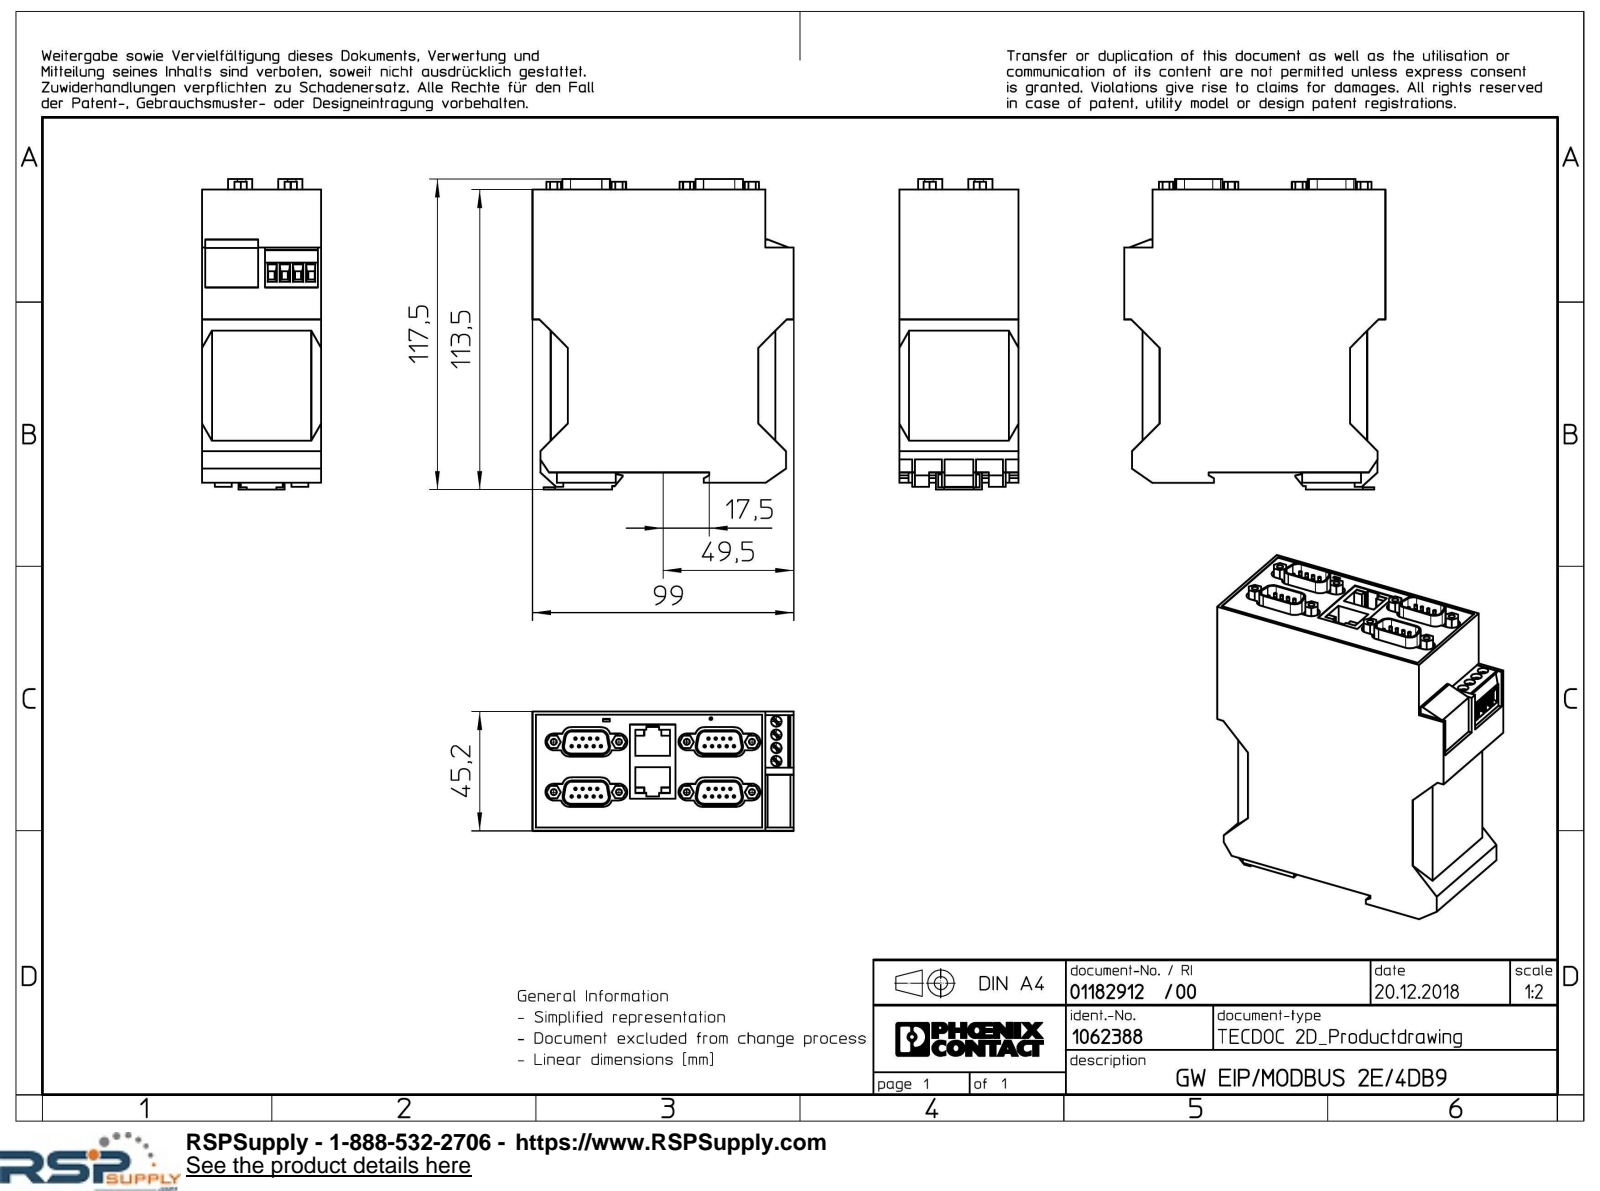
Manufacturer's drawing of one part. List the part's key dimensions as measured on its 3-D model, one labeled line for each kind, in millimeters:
Part name (STEP PRODUCT): GW_EIP_MODBUS_2E_4DB9-select
STEP written by: Creo Elements/Direct Modeling 18.1I 14-Aug-2016 (C) Parametric Technology GmbH (AUTOMOTIVE_DESIGN)
Units: millimetres
Bodies: 1 solid, 568 faces (414 planar, 154 cylindrical, 0 other)
Overall size (bounding box): 117.5 × 99 × 45.2
Volume: 437 141 mm³ · Surface area: 45 719 mm²
Round holes (diameter × count): ⌀2.29 ×8, ⌀4 ×4, ⌀1.08 ×1
Round bosses / shafts (diameter × count): ⌀1 ×36
Partial cylindrical surfaces — rounded edges, fillets, slot ends (radius × count): R3.17 ×24, R2.54 ×16, R3.04 ×16
Main face-to-face distances: 45.2, 4, 92.05, 6.95, 106.8, 85.1, 110.8, 3.75, 2, 88.3
Hole centre spacings: 19, 24.74, 31.19, 50.4, 53.86, 5, 10, 25.66
